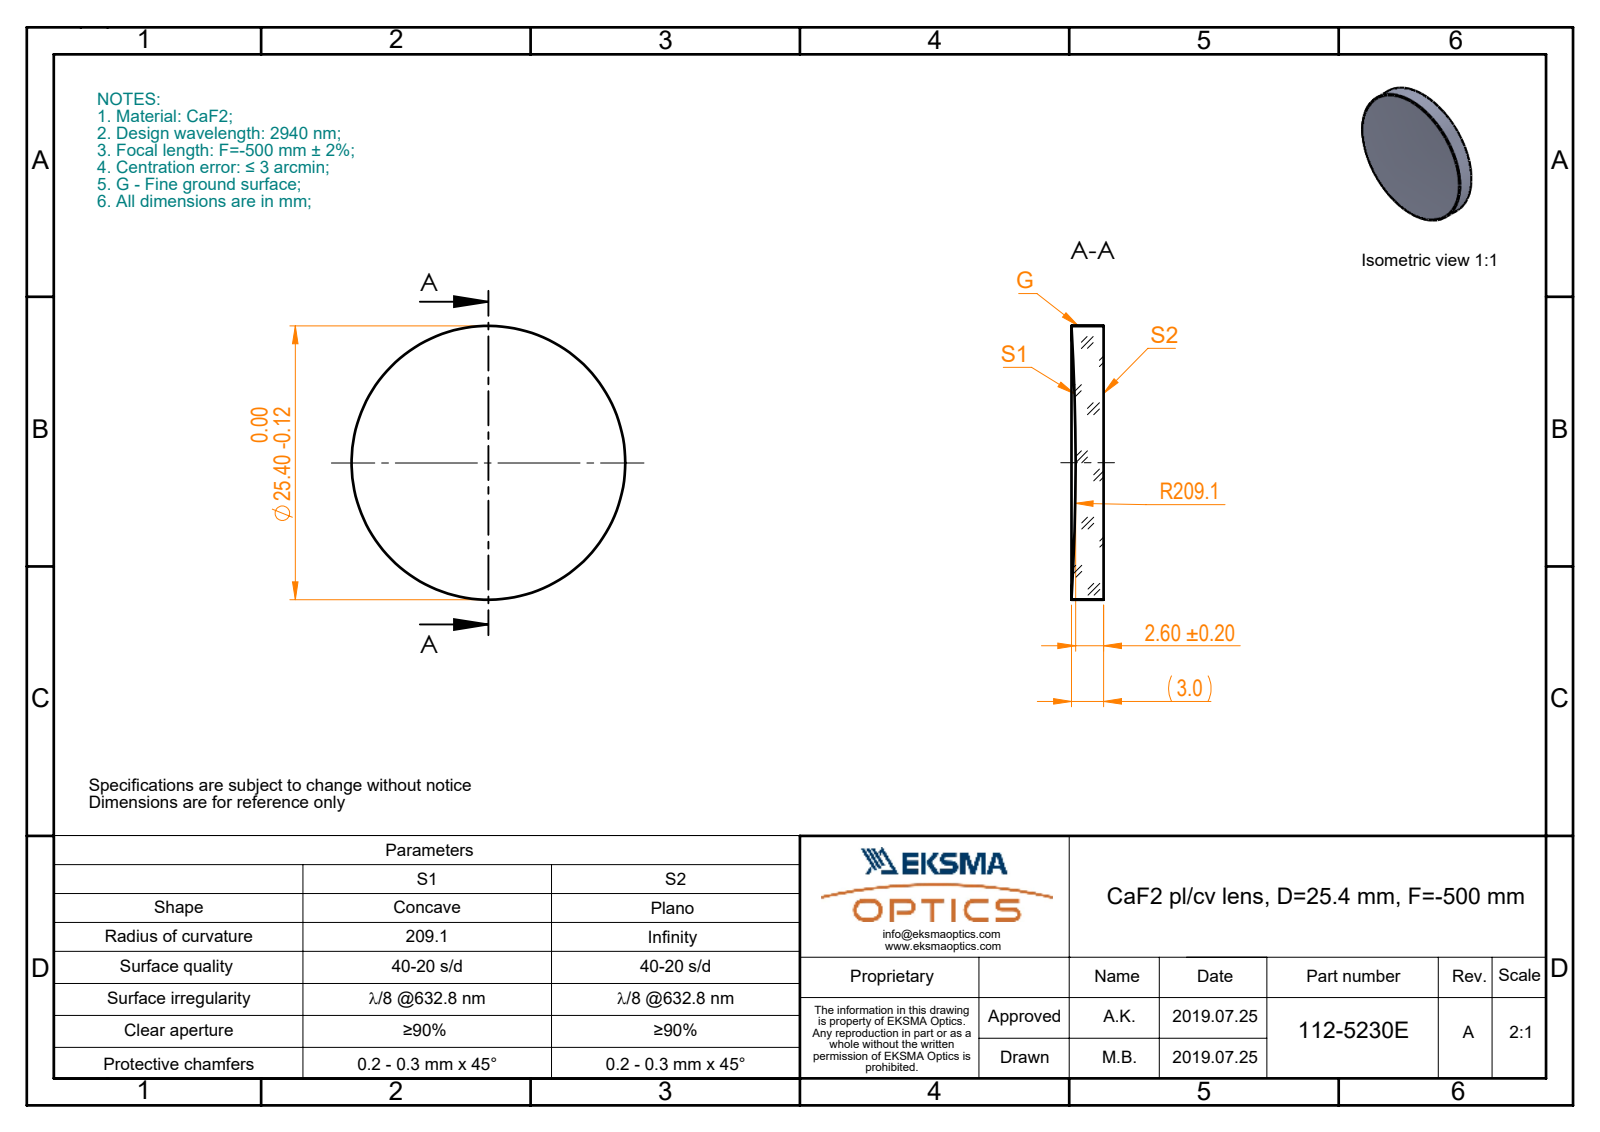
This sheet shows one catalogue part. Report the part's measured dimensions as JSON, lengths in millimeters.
{"part_name": "112-5230E CaF2 pl-cv 12.7 F-500", "step_written_by": "SolidWorks 2017 (CONFIG_CONTROL_DESIGN)", "units": "millimeters", "bodies": {"solids": 1, "faces": 5, "planar": 1, "cylindrical": 2, "other": 2}, "overall_size": [25.4, 25.4, 2.99], "volume_mm3": 1415, "surface_area_mm2": 1252, "round_bosses_or_shafts": [[25.4, 1]]}
